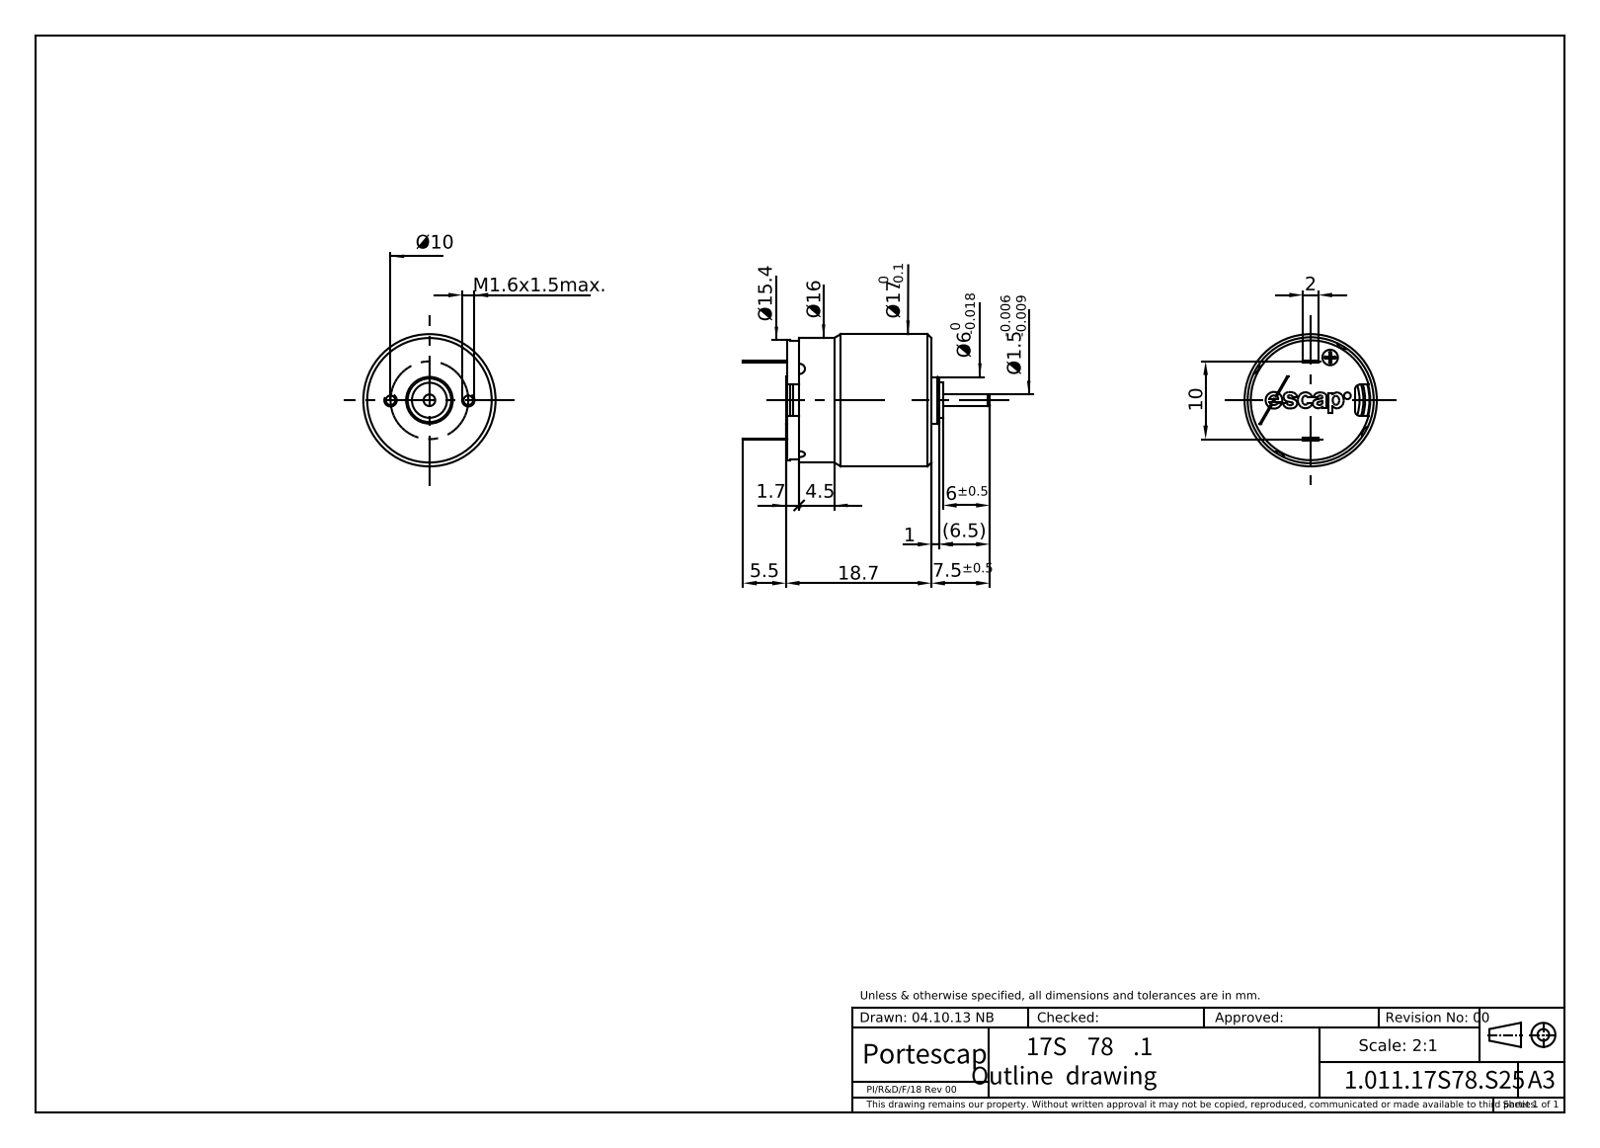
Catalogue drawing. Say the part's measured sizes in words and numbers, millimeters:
The part is named "17S_78_209E". Its 3-D file was written by "PRO/ENGINEER BY PARAMETRIC TECHNOLOGY CORPORATION, 2014310 (CONFIG_CONTROL_DESIGN)". It is 2 solids with 375 faces: 312 planar, 35 cylindrical and 28 other. Overall it measures 31.7 by 17 by 17 millimeters. Its volume is 4 080 cubic millimeters and its surface area 1 558 square millimeters. Round holes: 2 of diameter 1.25, 1 of diameter 0.6, 1 of diameter 2. Round bosses or shafts: 1 of diameter 17, 1 of diameter 16, 1 of diameter 15.4, 1 of diameter 15.3, 1 of diameter 6, 1 of diameter 5, 1 of diameter 1.5. Partial cylindrical surfaces (rounded edges, fillets, slot ends): 2 of radius 0.1, 2 of radius 0.2, 2 of radius 0.5, 2 of radius 0.6, 1 of radius 6.3. The main face-to-face distances are 18.7, 1.7, 10, 17, 1.5, 1.6, 17.1, 18.6, 20.2, 18.5. The hole center spacings are 0.5, 5.59, 6.04, 9.3, 10, 10.01.
